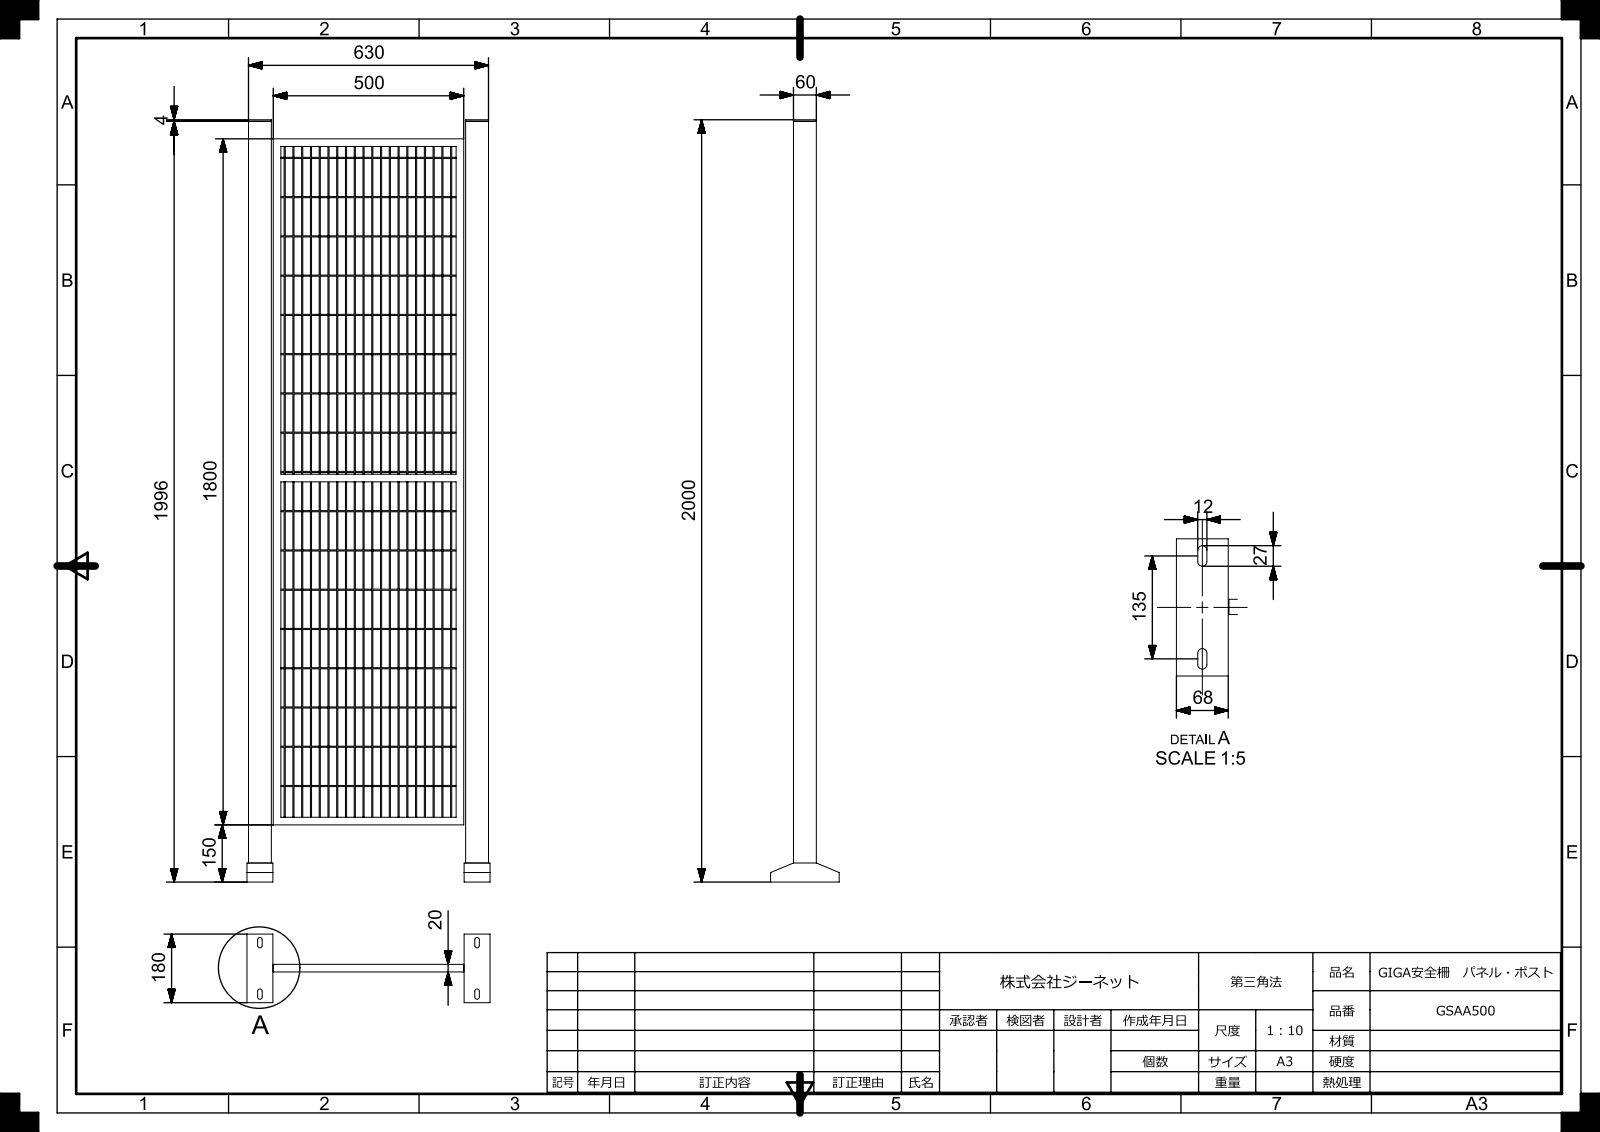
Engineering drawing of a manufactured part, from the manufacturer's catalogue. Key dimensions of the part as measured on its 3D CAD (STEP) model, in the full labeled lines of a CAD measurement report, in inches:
Part name (STEP PRODUCT): post_5; GSAA500_1; GSAA500_202104
STEP written by: SIEMENS PLM Software NX 12.0 (AUTOMOTIVE_DESIGN)
Units: inches
Bodies: 42 solids, 183 faces (136 planar, 47 cylindrical, 0 other)
Overall size (bounding box): 78.74 × 25.118 × 7.087
Volume: 1 059 in³ · Surface area: 2 875 in²
Round bosses / shafts (diameter × count): ⌀0.118 ×37
Partial cylindrical surfaces — rounded edges, fillets, slot ends (radius × count): R0.236 ×8
Main face-to-face distances: 2.362, 22.441, 0.787, 24.803, 20.079, 1.55, 0.813, 0.762, 1.6, 2.559
